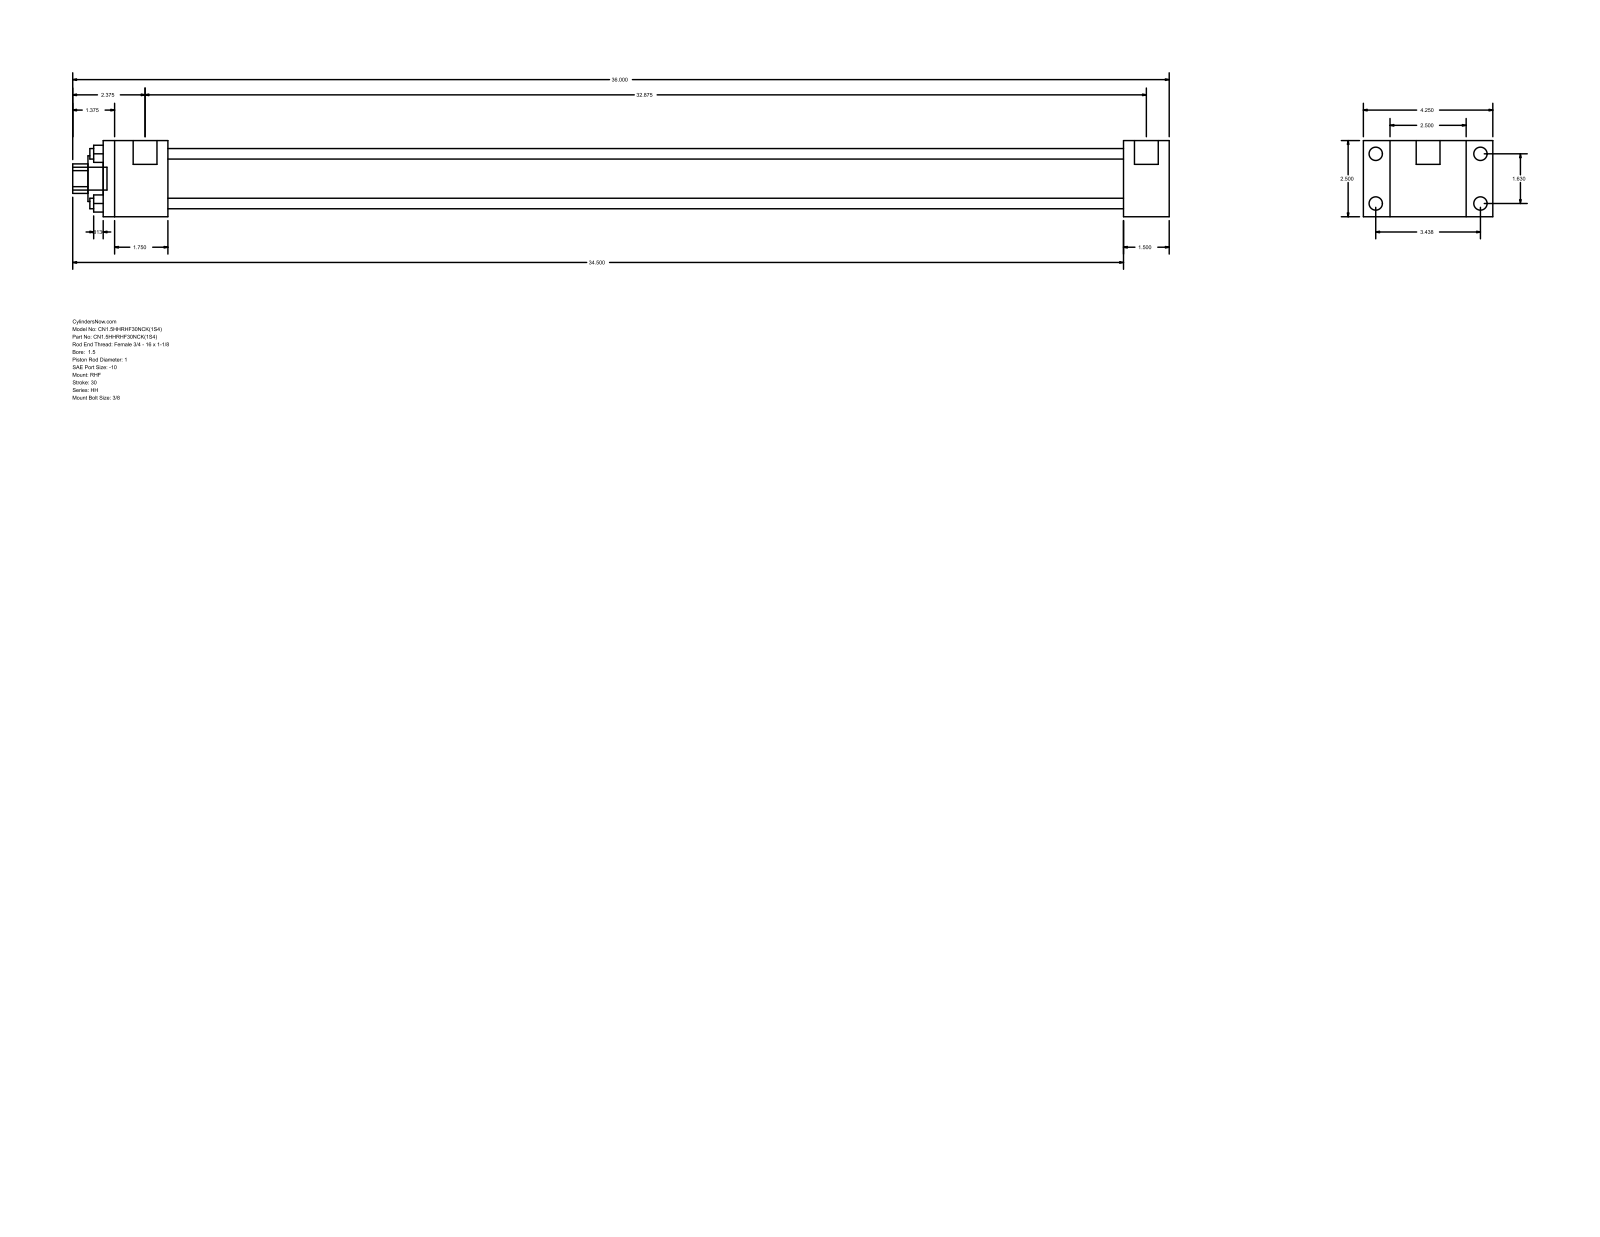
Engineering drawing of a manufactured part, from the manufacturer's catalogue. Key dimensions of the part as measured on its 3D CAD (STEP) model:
Part name (STEP PRODUCT): HH_RHF__0150_1
STEP written by: GSSL Pune (CONFIG_CONTROL_DESIGN)
Units: millimetres
Bodies: 0 solids, 88 faces (60 planar, 28 cylindrical, 0 other)
Overall size (bounding box): 914.4 × 107.95 × 63.5
Round holes (diameter × count): ⌀8.76 ×4, ⌀25.4 ×1, ⌀38.1 ×1, ⌀44.45 ×1
Round bosses / shafts (diameter × count): ⌀11.13 ×4, ⌀5.56 ×4, ⌀19.84 ×2, ⌀19.05 ×1
Partial cylindrical surfaces — rounded edges, fillets, slot ends (radius × count): R12.29 ×1
Main face-to-face distances: 63.5, 22.23, 85.73, 38.1, 107.96, 796.92, 835.02, 53.98, 850.9, 889
Hole centre spacings: 29.27, 41.4, 58.55
